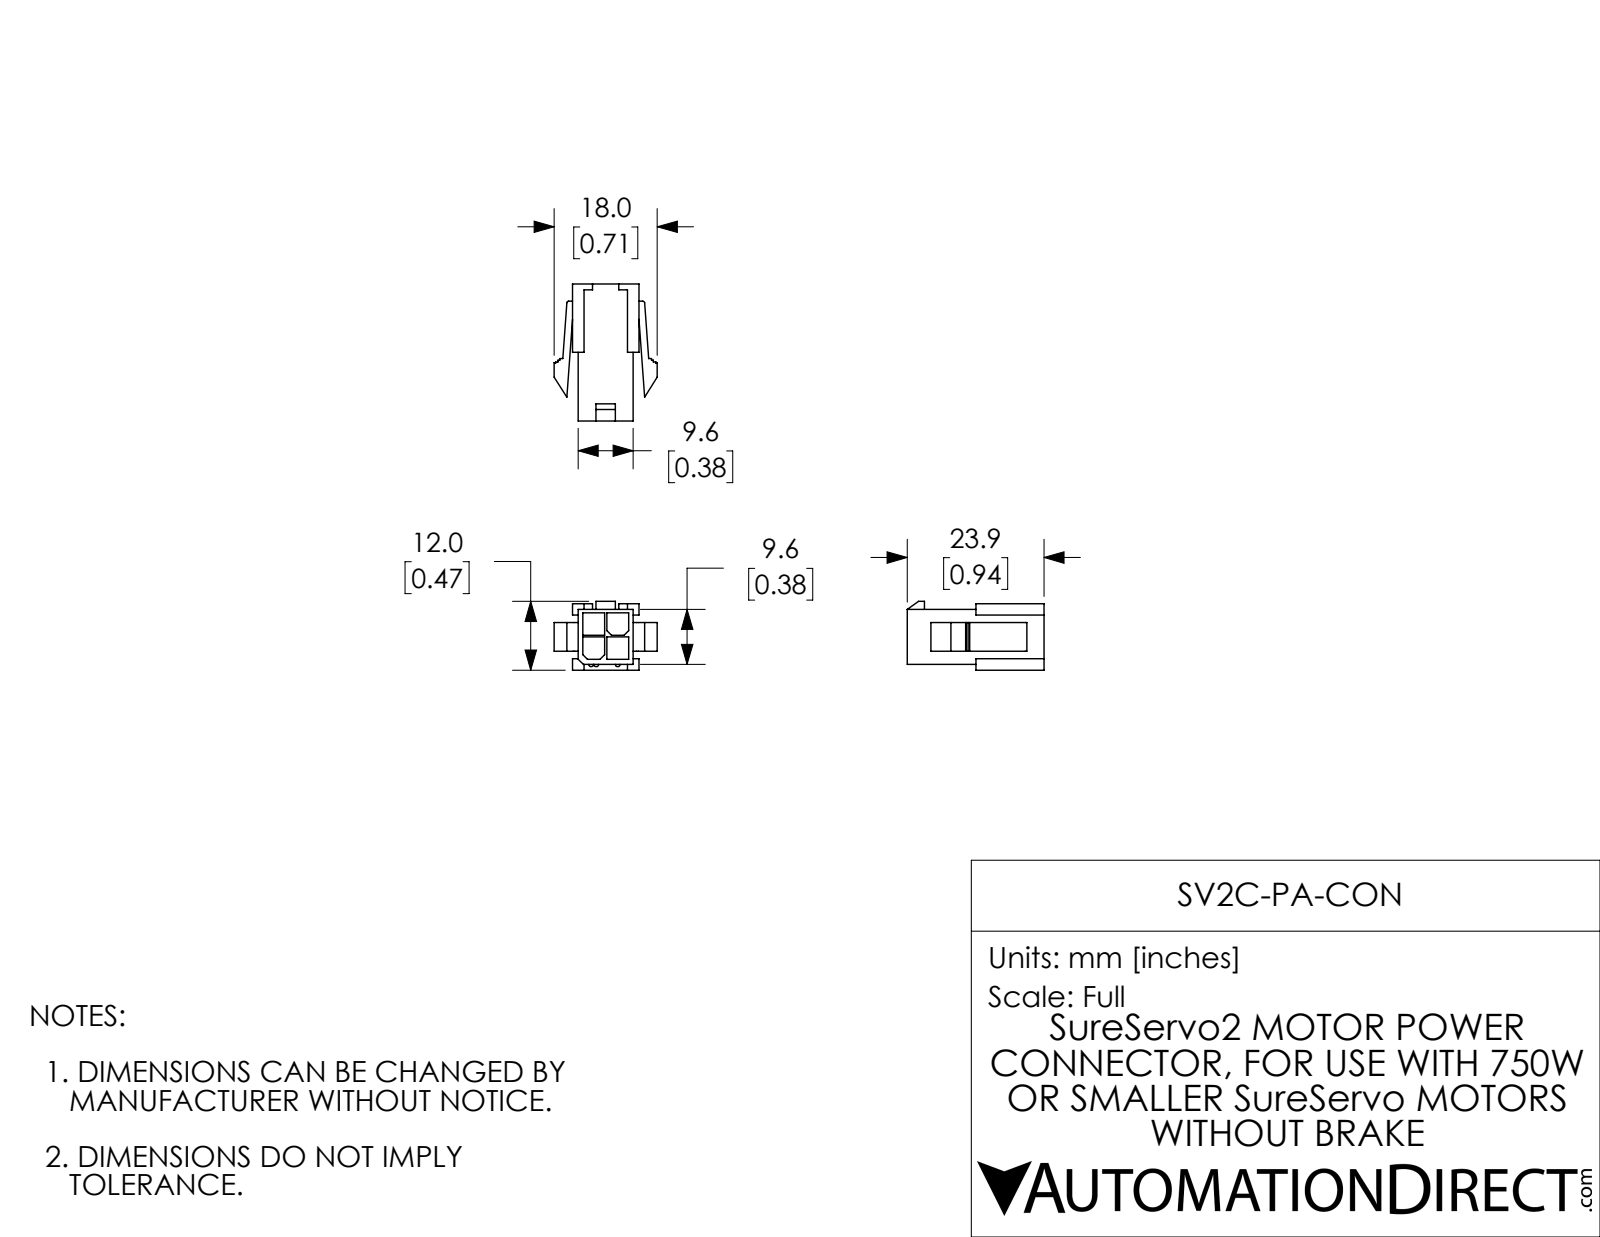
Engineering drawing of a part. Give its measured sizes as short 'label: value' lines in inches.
name: pa-con
written by: SolidWorks 2017 (AUTOMOTIVE_DESIGN)
unit: in
bodies: 1 solid, 116 faces (109 planar, 7 cylindrical, 0 other)
size: 0.941 × 0.709 × 0.472
volume: 0.075 in³; area: 4.838 in²
rounds: 4× R0.012, 3× R0.016
face distances: 0.165, 0.378, 0.197, 0.15, 0.346, 0.189, 0.031, 0.181, 0.039, 0.154
